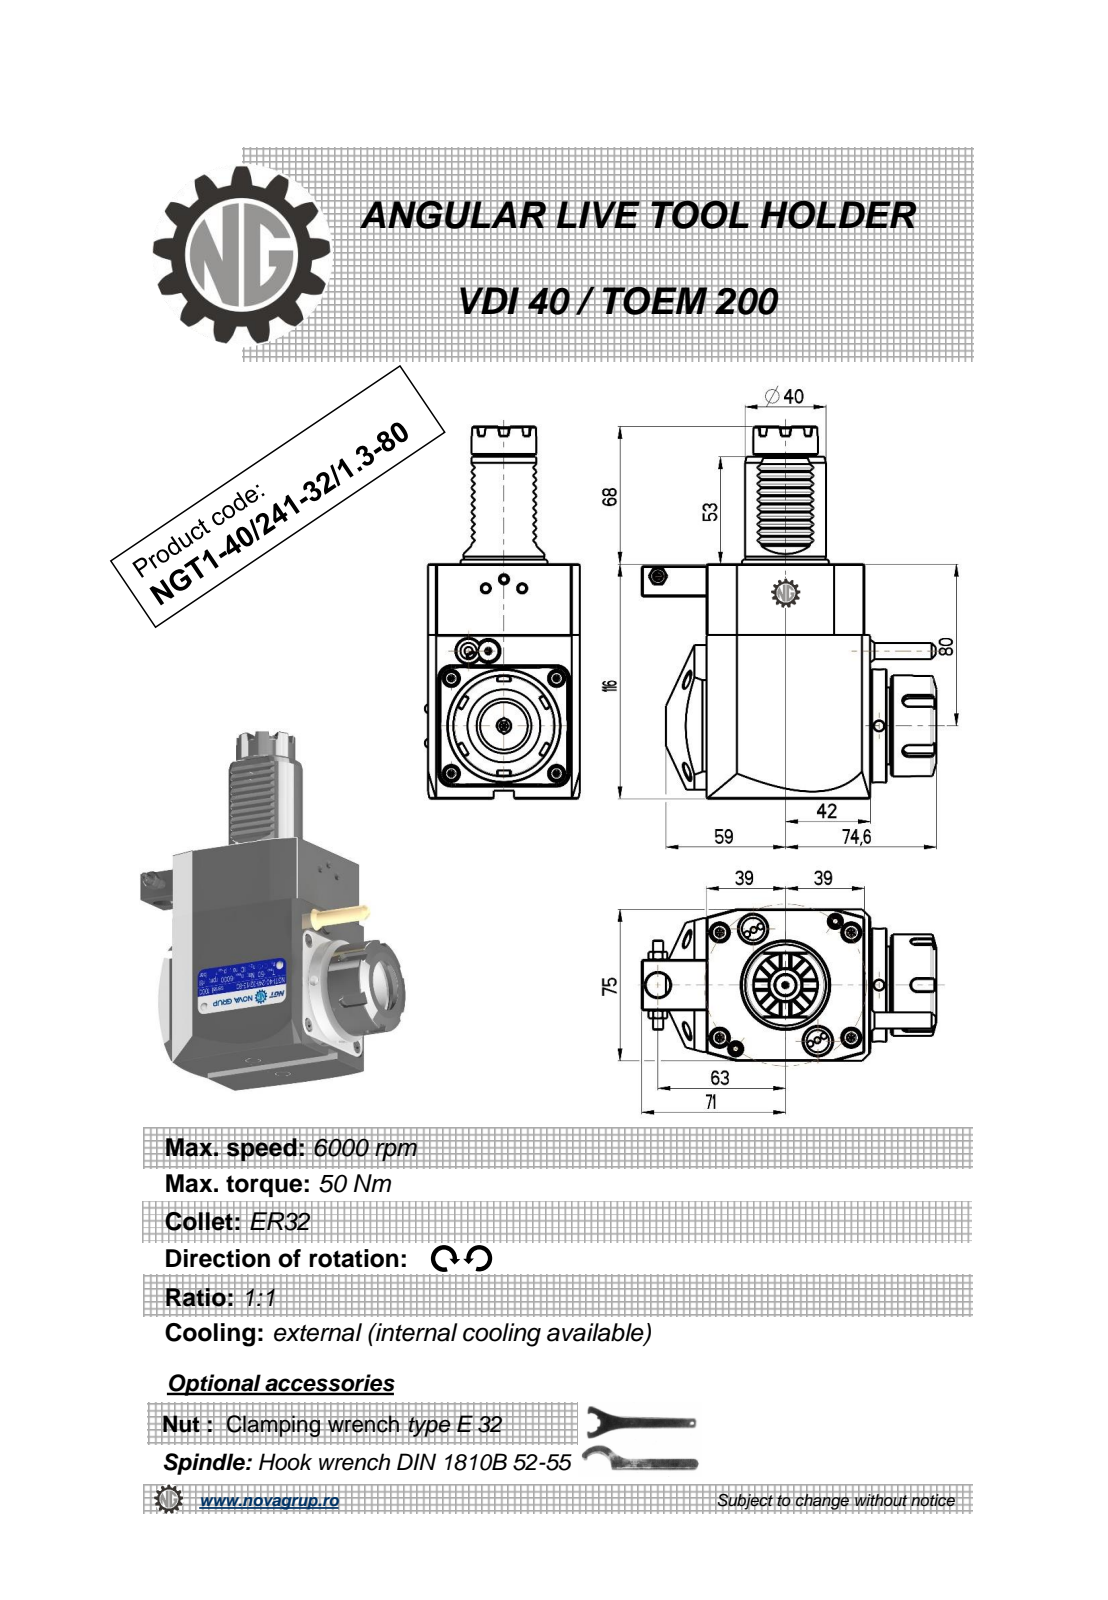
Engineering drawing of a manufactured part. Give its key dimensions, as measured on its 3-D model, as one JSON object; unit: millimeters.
{"part_name": "NGT1_40_241_32_1_3_80", "step_written_by": "PRO/ENGINEER BY PARAMETRIC TECHNOLOGY CORPORATION, 2010280 (CONFIG_CONTROL_DESIGN)", "units": "millimeters", "bodies": {"solids": 1, "faces": 535, "planar": 263, "cylindrical": 94, "other": 178}, "overall_size": [184, 145.6, 75], "volume_mm3": 877855, "surface_area_mm2": 72515, "round_holes": [[5, 3], [3, 1], [4.2, 1], [9.5, 1], [12, 1], [27, 1]], "round_bosses_or_shafts": [[56, 1], [50, 1], [43, 1], [40, 1], [32, 1], [17.2, 1], [10, 1], [8.96, 1]], "partial_cylinders_radius": [[0.3, 20], [0.26, 12], [0.2, 6], [3, 5], [40, 1]], "face_to_face_distances": [75, 116, 78, 81, 3, 80.8, 2.8, 7.5, 11, 0.5], "hole_center_spacings": [39.58, 40.93, 72.5, 109.25, 131.95]}
